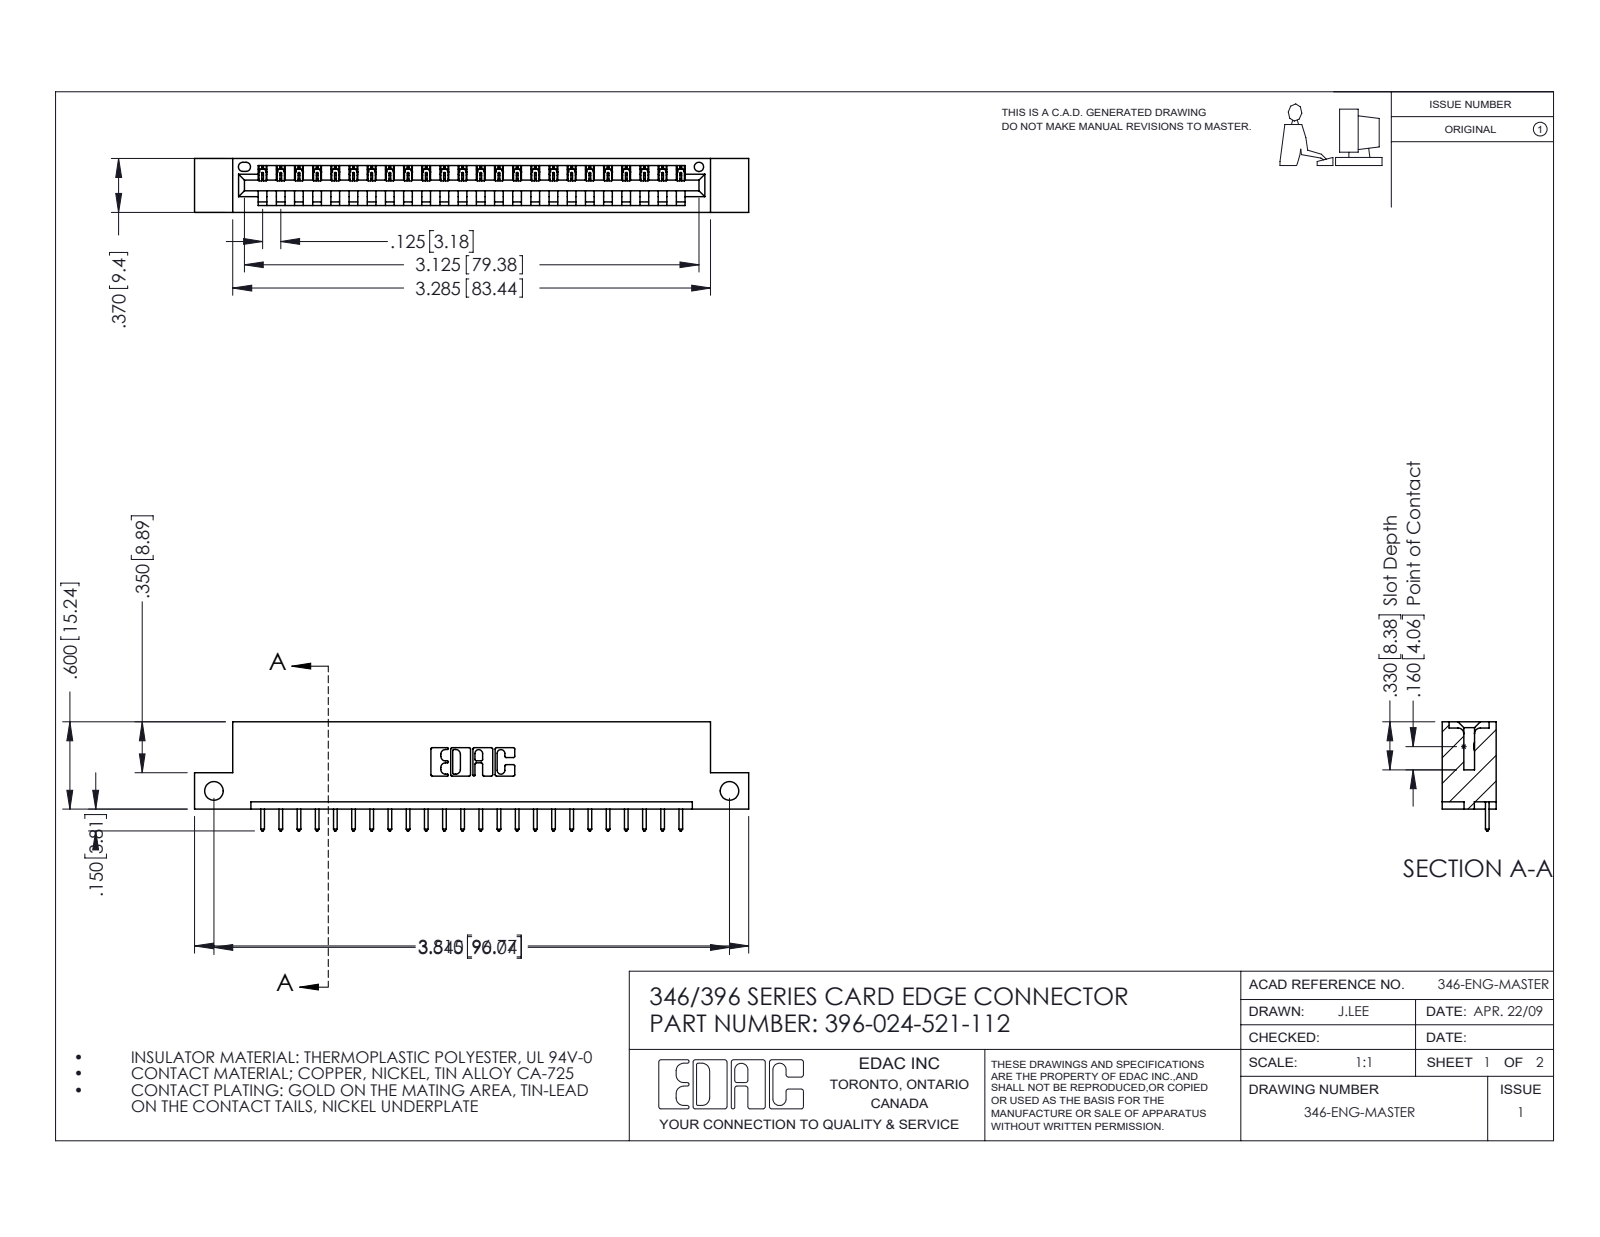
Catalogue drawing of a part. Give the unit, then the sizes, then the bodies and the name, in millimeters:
Units: millimetres
Overall size (bounding box): 96.8 × 19.1 × 9.4
Round holes (diameter × count): ⌀3.3 ×2, ⌀1.6 ×1
Partial cylindrical surfaces — rounded edges, fillets, slot ends (radius × count): R0.2 ×48, R0.3 ×48, R0.3 ×22, R0.2 ×6, R0.8 ×6, R0.7 ×3, R0.8 ×2, R1 ×2
Main face-to-face distances: 1.2, 8.2, 9.4, 6.4, 1.8, 7.6, 0.6, 3.8, 5.6, 2.5
Hole centre spacings: 90
Volume: 8 980 mm³ · Surface area: 10 620 mm²
Bodies: 25 solids, 1514 faces (1036 planar, 478 cylindrical, 0 other)
Part name (STEP PRODUCT): 345-292-001_345-293-121; 346 Part_Flush Mounting Lugs - Side Mount; 396-024-521-112
STEP written by: SolidWorks 2016 (CONFIG_CONTROL_DESIGN)
